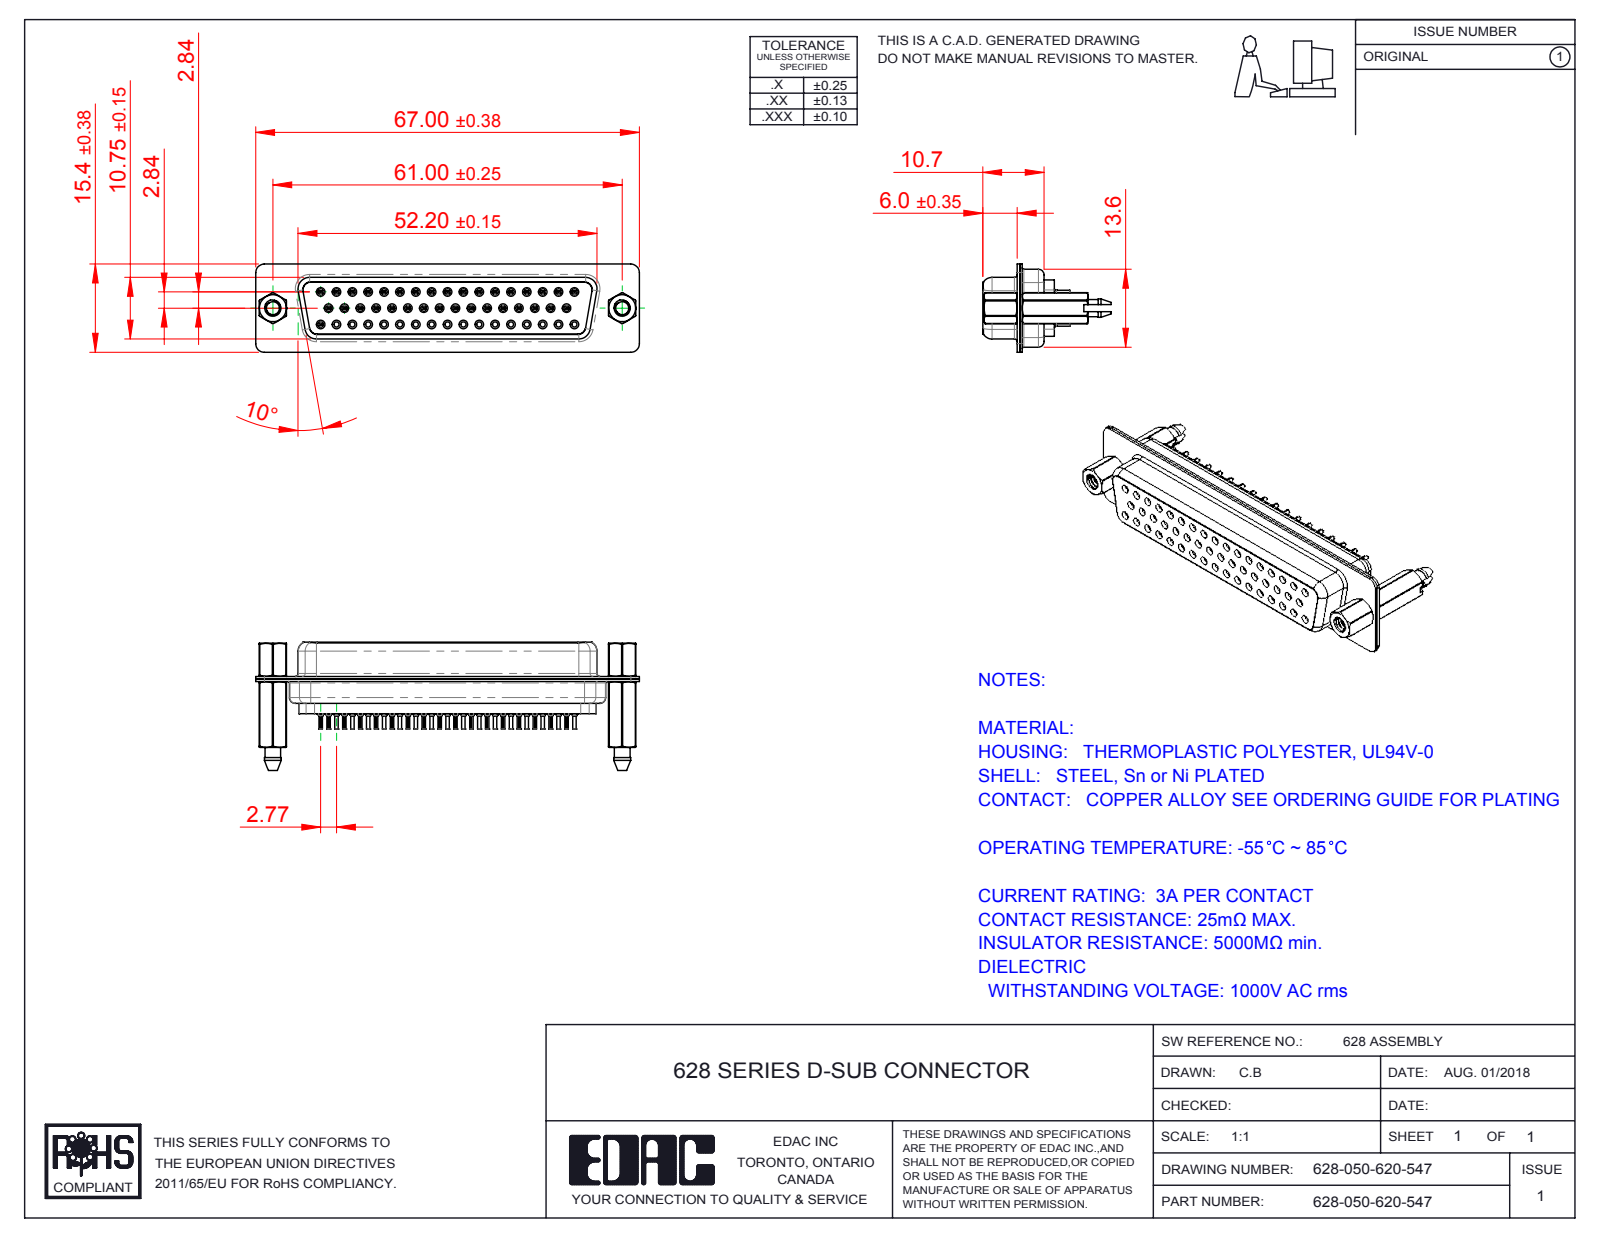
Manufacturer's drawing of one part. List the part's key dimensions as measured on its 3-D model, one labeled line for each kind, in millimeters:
Part name (STEP PRODUCT): 628 Contact Row 1_20L; 628 Contact Row 3_20L; 628 Shell Front_50 Contacts; 628 Housing_50 LP (+5 more)
STEP written by: SolidWorks 2016 (CONFIG_CONTROL_DESIGN)
Units: millimetres
Bodies: 41 solids, 5039 faces (1223 planar, 1525 cylindrical, 2291 other)
Overall size (bounding box): 67 × 22.4 × 15.4
Volume: 7 065 mm³ · Surface area: 14 684 mm²
Round holes (diameter × count): ⌀0.9 ×50, ⌀1.6 ×50, ⌀0.2 ×34, ⌀0.8 ×34, ⌀1.1 ×34, ⌀1.7 ×17, ⌀1.5 ×16, ⌀2 ×16, ⌀2.26 ×2, ⌀2.29 ×2, ⌀4 ×2, ⌀4.8 ×2
Round bosses / shafts (diameter × count): ⌀2 ×34, ⌀1.5 ×34, ⌀1.2 ×34, ⌀0.6 ×34, ⌀4.9 ×2, ⌀2.79 ×2
Partial cylindrical surfaces — rounded edges, fillets, slot ends (radius × count): R0.1 ×68, R0.28 ×33, R1.5 ×18, R2 ×12, R1.35 ×8, R1.6 ×6, R0.25 ×4, R0.5 ×4
Main face-to-face distances: 0.45, 0.4, 10.3, 0.9, 6.05, 6.5, 6, 6.45, 12.5, 11.33
Hole centre spacings: 3.16, 2.77, 5.54, 8.31, 11.08, 13.85, 16.62, 19.39
